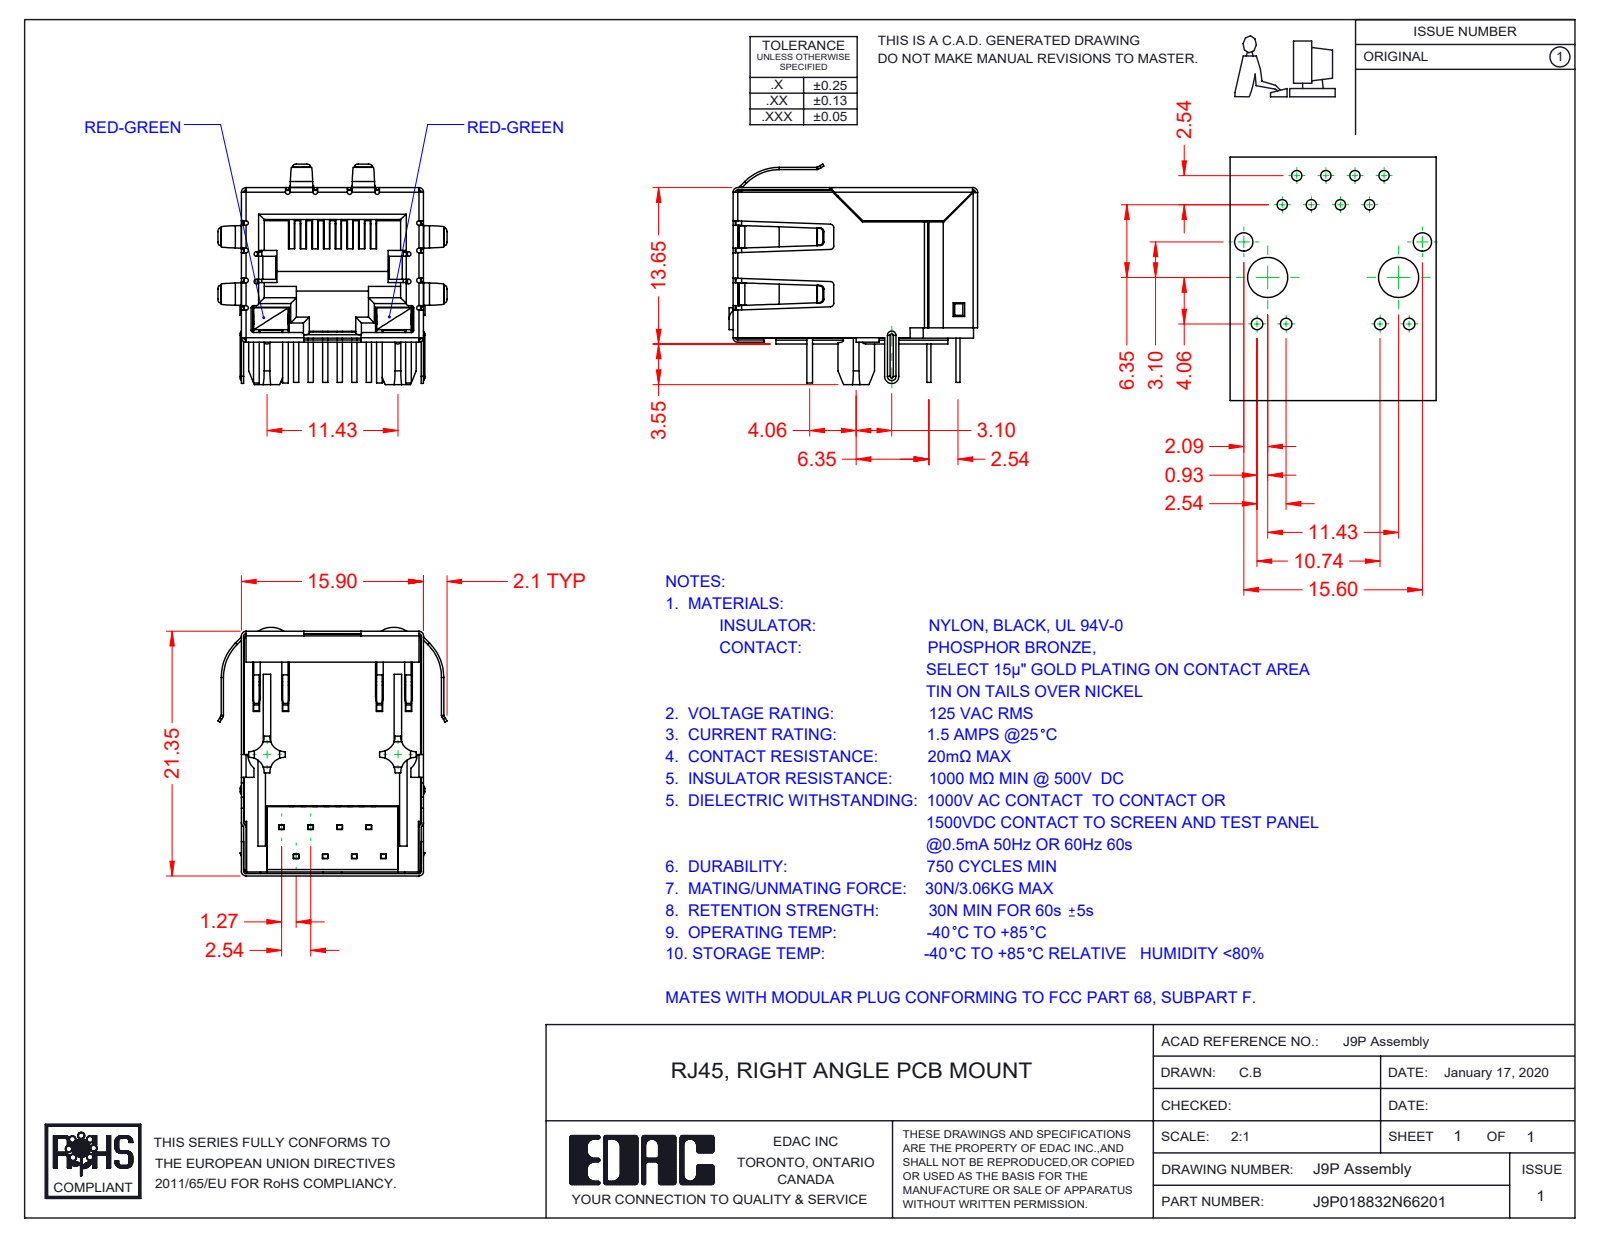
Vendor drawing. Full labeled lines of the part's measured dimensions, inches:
Part name (STEP PRODUCT): 9P-LED Insulator; 9P-LED Contact Lock; 9P-LED Shield; 9P-LED LED RH_6-Red-Green (+4 more)
STEP written by: SolidWorks 2016 (CONFIG_CONTROL_DESIGN)
Units: inches
Bodies: 13 solids, 1476 faces (1042 planar, 340 cylindrical, 94 other)
Overall size (bounding box): 0.854 × 0.787 × 0.758
Volume: 0.164 in³ · Surface area: 11.65 in²
Partial cylindrical surfaces — rounded edges, fillets, slot ends (radius × count): R0.008 ×39, R0.02 ×22, R0.012 ×20, R0.016 ×16, R0.051 ×8, R0.009 ×5, R0.004 ×4, R0.012 ×4
Main face-to-face distances: 0.608, 0.618, 0.616, 0.014, 0.021, 0.61, 0.487, 0.024, 0.055, 0.023
